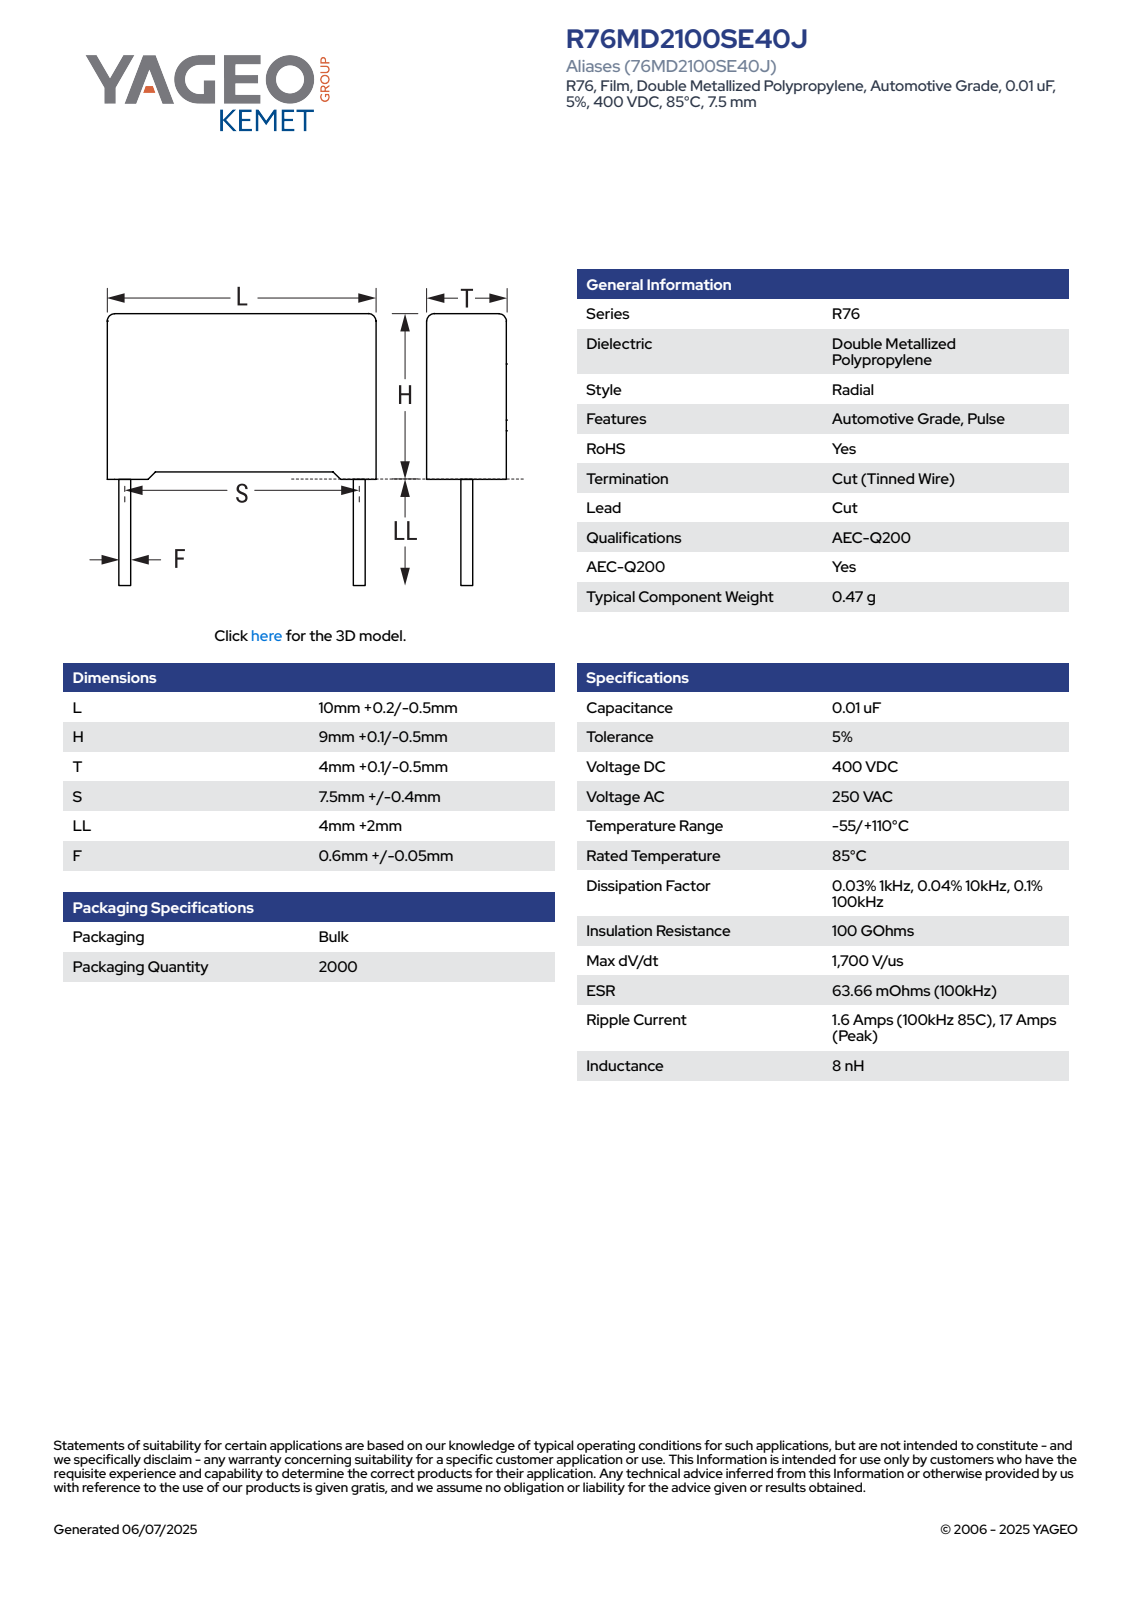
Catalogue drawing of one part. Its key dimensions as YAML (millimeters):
part_name: "CFR_RB2_10X9X4_L10.2H9.1T4.1S7.5LL6F0.65"
step_written_by: "SolidWorks 2021 (AUTOMOTIVE_DESIGN)"
units: millimeters
bodies: {solids: 4, faces: 85, planar: 77, cylindrical: 8, other: 0}
overall_size: [15.1, 10.2, 4.11]
volume: 358
surface_area: 387
round_bosses_or_shafts:
  - {diameter: 0.65, count: 2}
partial_cylinders:
  - {radius: 0.5, count: 4}
face_to_face_distances: [4.1, 10.2, 8.35, 0.34, 3.76, 0.75, 9.1, 3.42, 9.86, 0.31]
